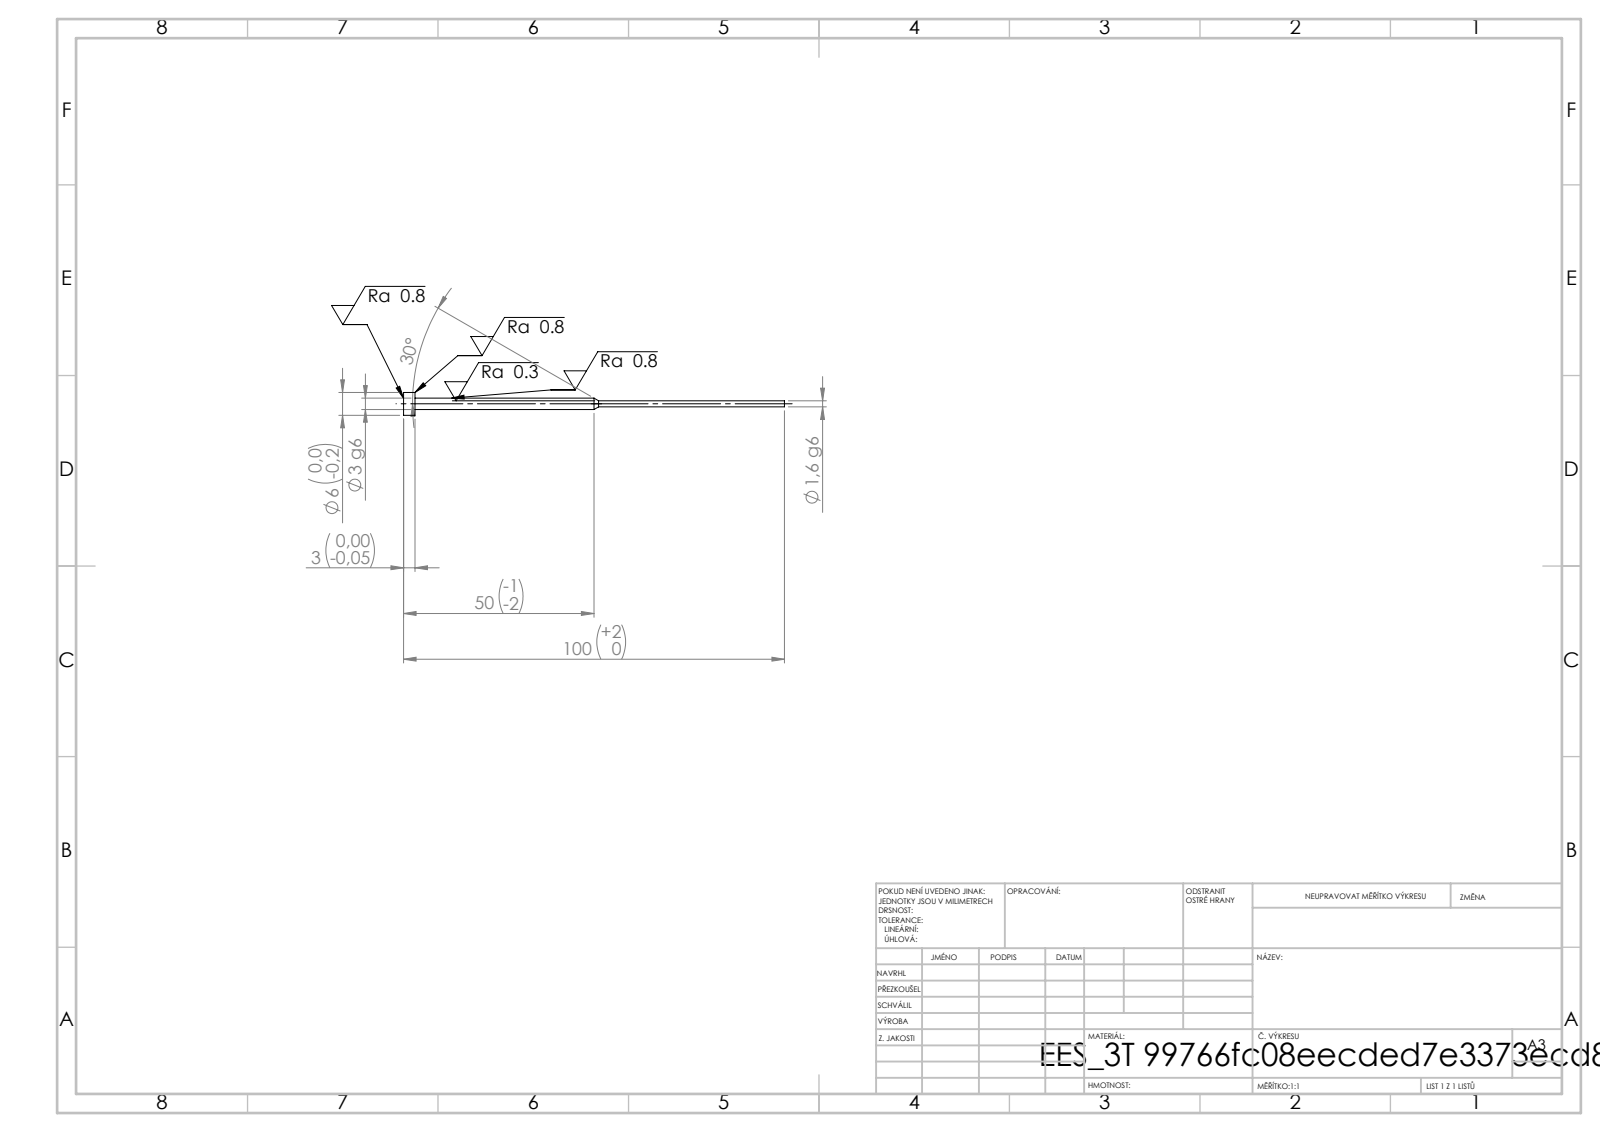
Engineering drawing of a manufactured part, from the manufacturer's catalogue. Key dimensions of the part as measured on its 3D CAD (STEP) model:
STEP written by: SolidWorks 2019 (CONFIG_CONTROL_DESIGN)
Units: millimetres
Bodies: 1 solid, 11 faces (3 planar, 6 cylindrical, 2 other)
Overall size (bounding box): 100 × 6 × 6
Volume: 520 mm³ · Surface area: 806 mm²
Round bosses / shafts (diameter × count): ⌀6 ×1, ⌀3 ×1, ⌀1.6 ×1
Main face-to-face distances: 3, 97, 100
